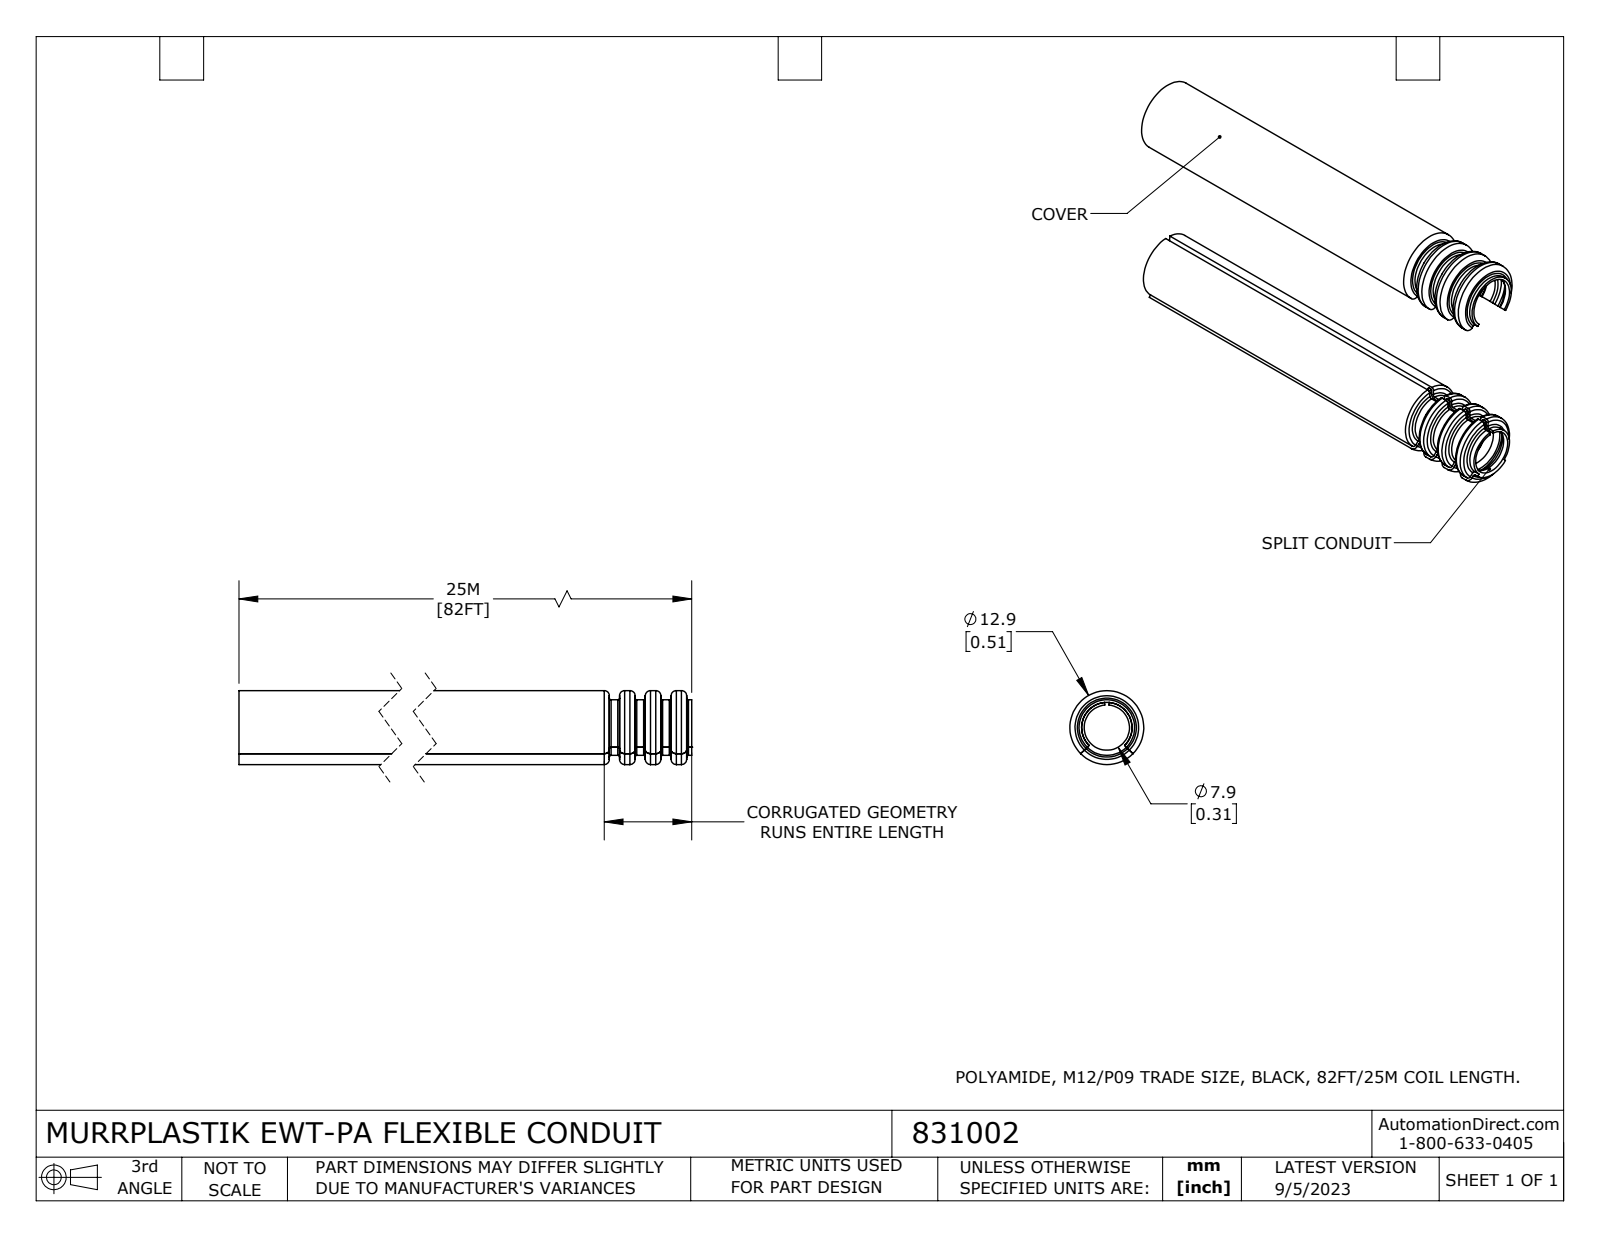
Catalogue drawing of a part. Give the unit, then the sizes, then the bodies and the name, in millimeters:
Units: millimetres
Overall size (bounding box): 80 × 12.9 × 12.9
Round holes (diameter × count): ⌀7.9 ×1, ⌀11.1 ×1
Round bosses / shafts (diameter × count): ⌀12.9 ×1, ⌀9.7 ×1
Partial cylindrical surfaces — rounded edges, fillets, slot ends (radius × count): R4.4 ×1, R6 ×1
Main face-to-face distances: 80
Volume: 5 820 mm³ · Surface area: 10 940 mm²
Bodies: 2 solids, 343 faces (10 planar, 107 cylindrical, 226 other)
Part name (STEP PRODUCT): 831002
STEP written by: SolidWorks 2021 (CONFIG_CONTROL_DESIGN)
